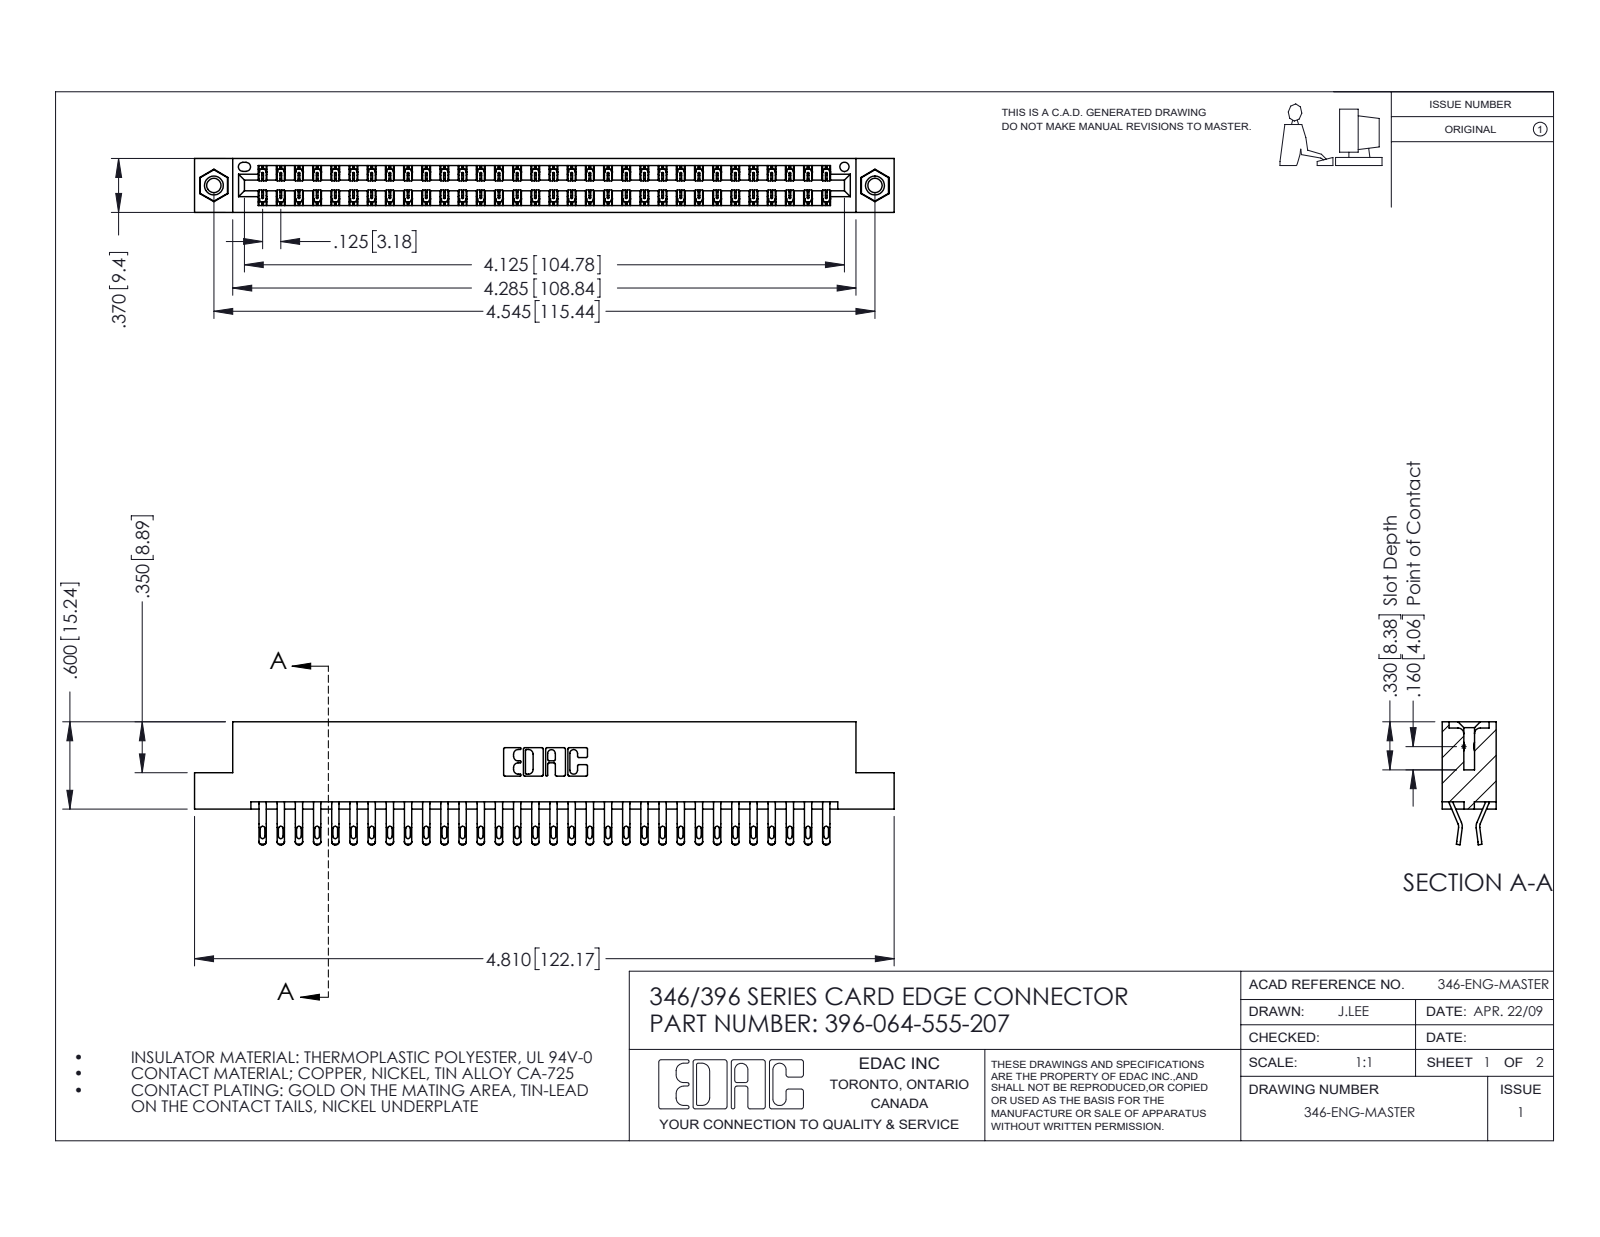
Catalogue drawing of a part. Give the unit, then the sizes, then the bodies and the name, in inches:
Units: inches
Overall size (bounding box): 4.81 × 0.845 × 0.37
Round holes (diameter × count): ⌀0.098 ×2, ⌀0.125 ×2, ⌀0.156 ×2, ⌀0.064 ×1
Round bosses / shafts (diameter × count): ⌀0.155 ×2
Partial cylindrical surfaces — rounded edges, fillets, slot ends (radius × count): R0.016 ×128, R0.02 ×128, R0.006 ×96, R0.01 ×22, R0.007 ×6, R0.031 ×6, R0.026 ×3, R0.01 ×2
Main face-to-face distances: 0.048, 0.322, 0.37, 0.25, 0.025, 0.072, 0.298, 0.275, 0.148, 0.222
Hole centre spacings: 0.246, 4.337, 4.545
Volume: 0.733 in³ · Surface area: 26.42 in²
Bodies: 67 solids, 3894 faces (2220 planar, 1658 cylindrical, 16 other)
Part name (STEP PRODUCT): 345-250-001_345-250-005-103; 345-292-001_555 Tail; 396-064-555-207; 346 Part_Flush Mounting Lugs - 0.156 Dia-TI
STEP written by: SolidWorks 2016 (CONFIG_CONTROL_DESIGN)
